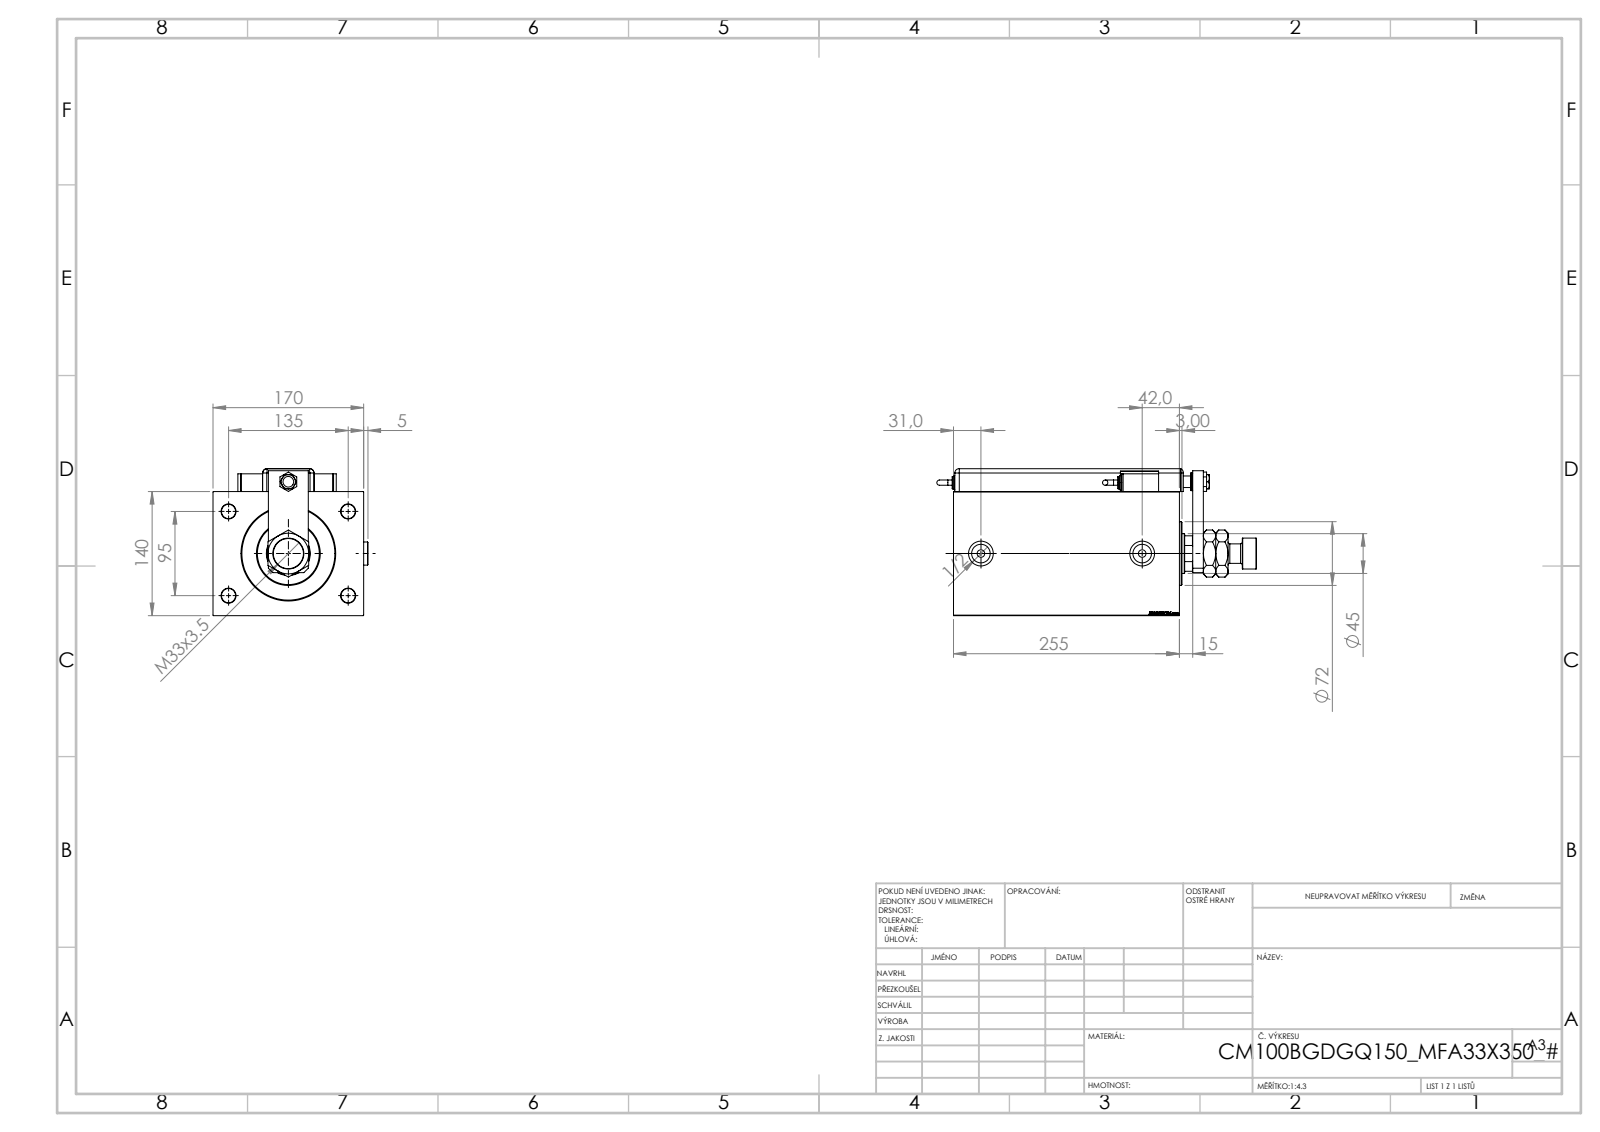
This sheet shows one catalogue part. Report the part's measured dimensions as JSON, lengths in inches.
{"part_name": "NUT_D13; MAGNETIC SWITCH Q; SWITCH Q; V450CM_B_Body (+8 more)", "step_written_by": "SolidWorks 2019 (CONFIG_CONTROL_DESIGN)", "units": "inches", "bodies": {"solids": 16, "faces": 1374, "planar": 658, "cylindrical": 131, "other": 585}, "overall_size": [14.203, 6.886, 6.528], "volume_in3": 328.2, "surface_area_in2": 771.5, "round_holes": [[0.63, 4], [0.157, 2], [0.315, 2], [0.335, 2], [0.825, 2], [1.102, 2], [0.472, 1], [0.512, 1], [0.551, 1], [1.24, 1], [1.299, 1], [1.772, 1]], "round_bosses_or_shafts": [[0.787, 3], [1.024, 2], [0.63, 2], [0.551, 2], [0.236, 2], [2.835, 1], [1.378, 1], [0.866, 1]], "partial_cylinders_radius": [[0.197, 9], [0.394, 1], [0.866, 1]], "face_to_face_distances": [5.512, 6.693, 0.118, 10.039, 1.024, 9.016, 0.591, 1.016, 6.528, 6.409], "hole_center_spacings": [3.25, 2.967, 3.74, 5.315, 5.715, 6.499, 0.787, 3.189]}
